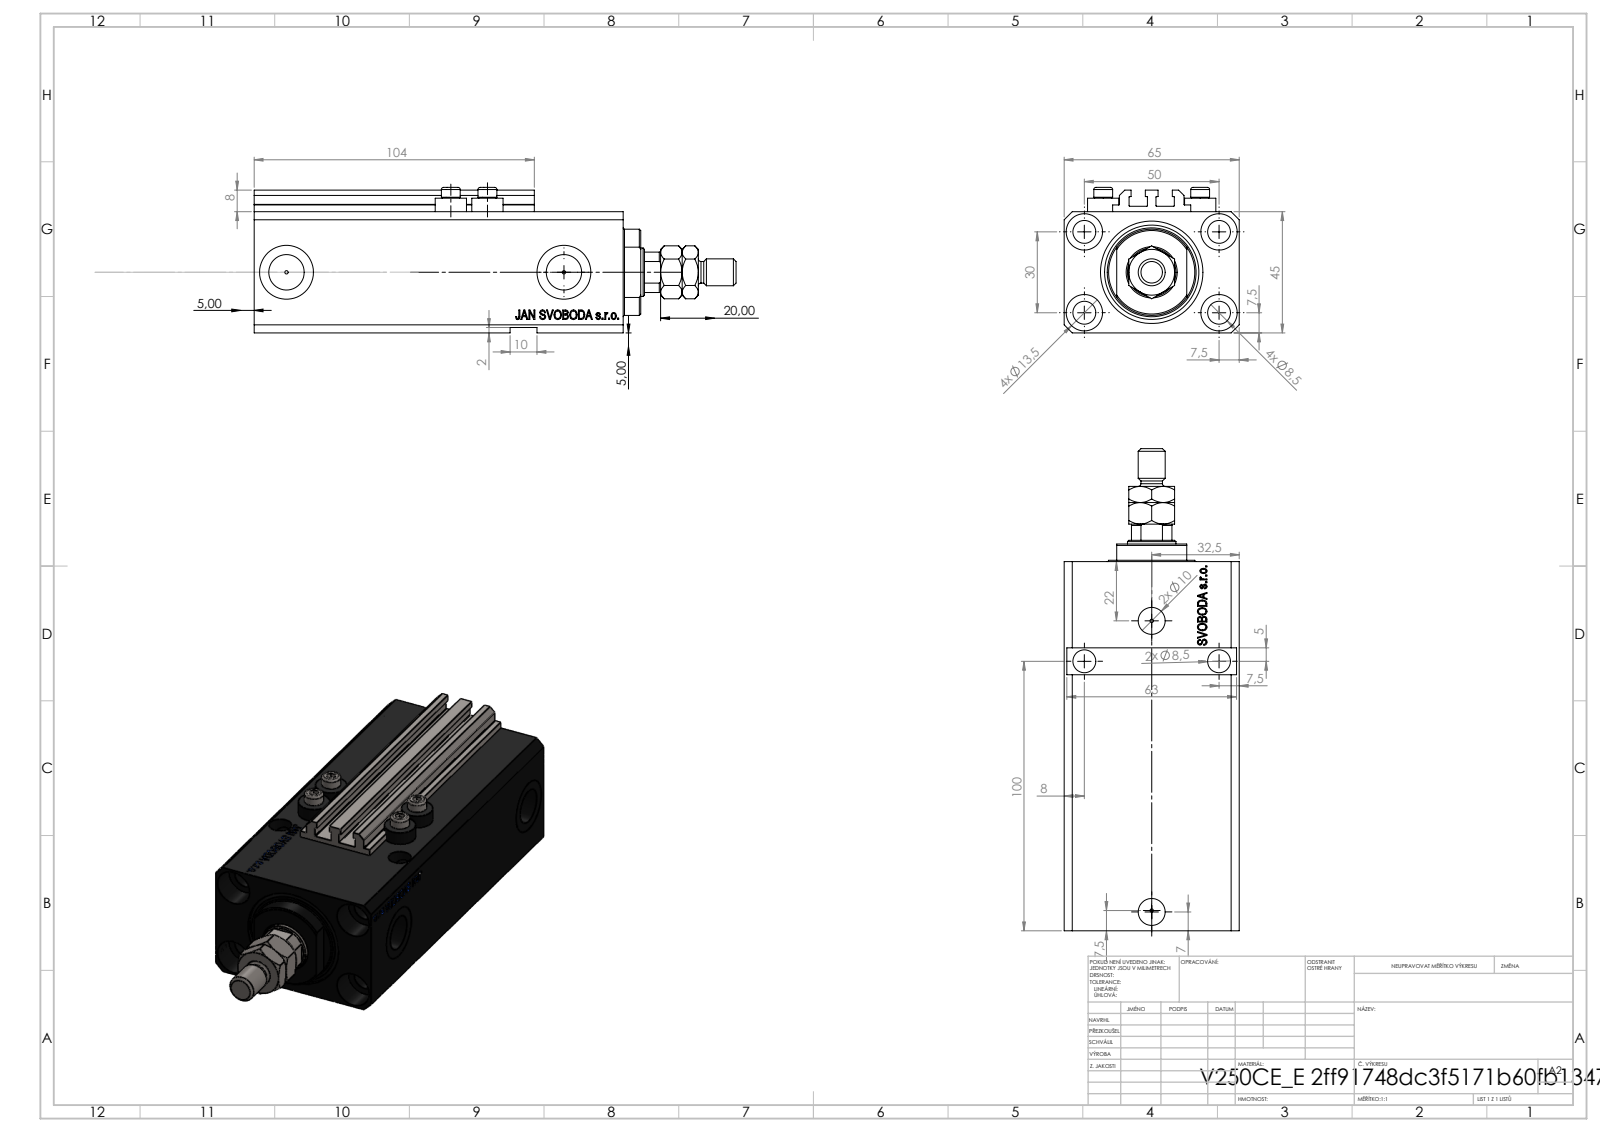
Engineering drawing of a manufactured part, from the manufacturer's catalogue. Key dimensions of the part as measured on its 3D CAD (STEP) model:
Part name (STEP PRODUCT): V250CE_VC_E; V250CE_E_Body; V250CE_C_VCP; ALLEN BOLT V250CE (+1 more)
STEP written by: SolidWorks 2019 (CONFIG_CONTROL_DESIGN)
Units: millimetres
Bodies: 9 solids, 1152 faces (530 planar, 162 cylindrical, 460 other)
Overall size (bounding box): 179 × 65 × 54
Volume: 351 364 mm³ · Surface area: 96 421 mm²
Round holes (diameter × count): ⌀8.5 ×9, ⌀1.25 ×4, ⌀4 ×4, ⌀13.5 ×4, ⌀10 ×2, ⌀13.16 ×2, ⌀20 ×2, ⌀18 ×1, ⌀25 ×1, ⌀38 ×1
Round bosses / shafts (diameter × count): ⌀11.6 ×4, ⌀7 ×4, ⌀10 ×1, ⌀8 ×1
Partial cylindrical surfaces — rounded edges, fillets, slot ends (radius × count): R0.2 ×10, R8.5 ×1, R16 ×1
Main face-to-face distances: 45, 65, 47, 14, 2, 123, 2.5, 10, 24, 20.4
Hole centre spacings: 29.15, 50, 13.6, 15.12, 27.89, 30, 33.61, 33.62
